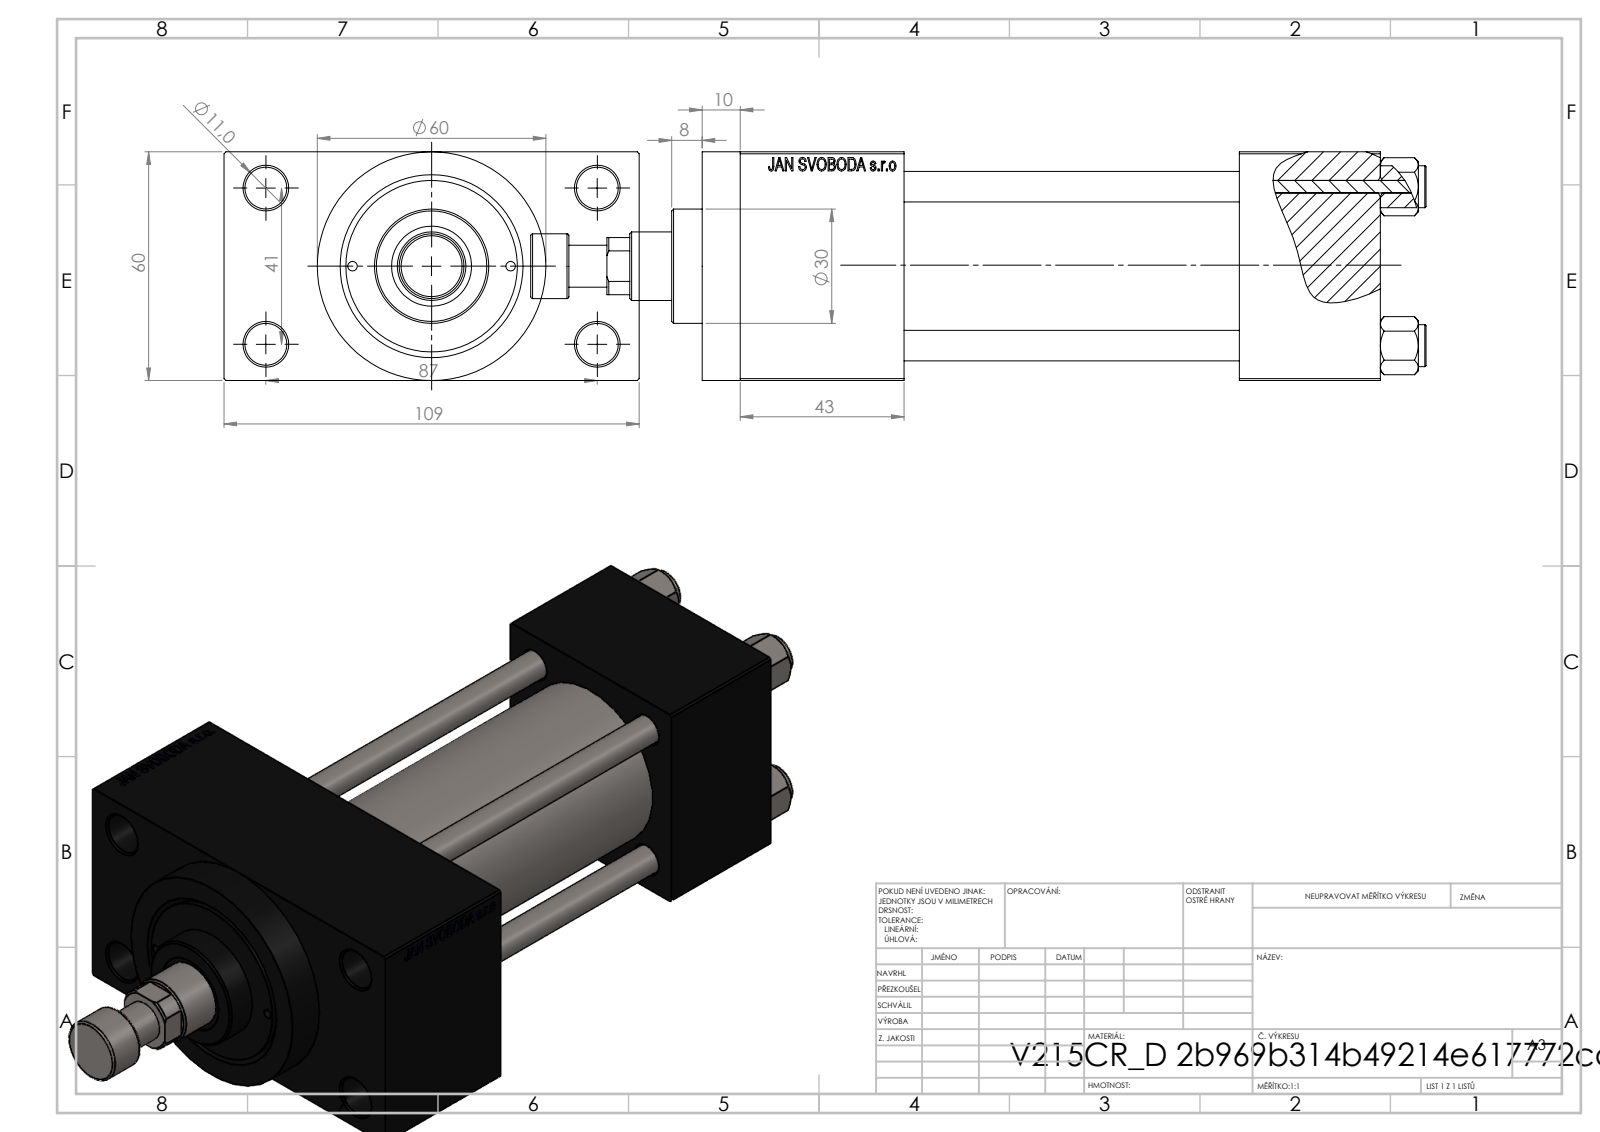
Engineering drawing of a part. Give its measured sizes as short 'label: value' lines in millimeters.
name: V215CR_ROD_END_F; V215CR_VCP_D; V215CR_D_Body; V215CR_D_TYCINKA (+2 more)
written by: SolidWorks 2019 (CONFIG_CONTROL_DESIGN)
unit: mm
bodies: 12 solids, 1123 faces (503 planar, 96 cylindrical, 524 other)
size: 235 × 109 × 60
volume: 541 349 mm³; area: 136 632 mm²
holes: 4× ⌀8, 4× ⌀11, 2× ⌀2.5, 2× ⌀7, 2× ⌀16.66, 2× ⌀24, 1× ⌀8.5, 1× ⌀18, 1× ⌀21, 1× ⌀31, 1× ⌀40, 1× ⌀45
bosses: 5× ⌀11, 1× ⌀60, 1× ⌀46, 1× ⌀30, 1× ⌀17
face distances: 60, 88, 24.5, 37, 84.5, 125, 168, 131, 43, 10
hole spacings: 20.85, 22.65, 29.49, 30.62, 41.7, 46.53, 47.15, 48.09
